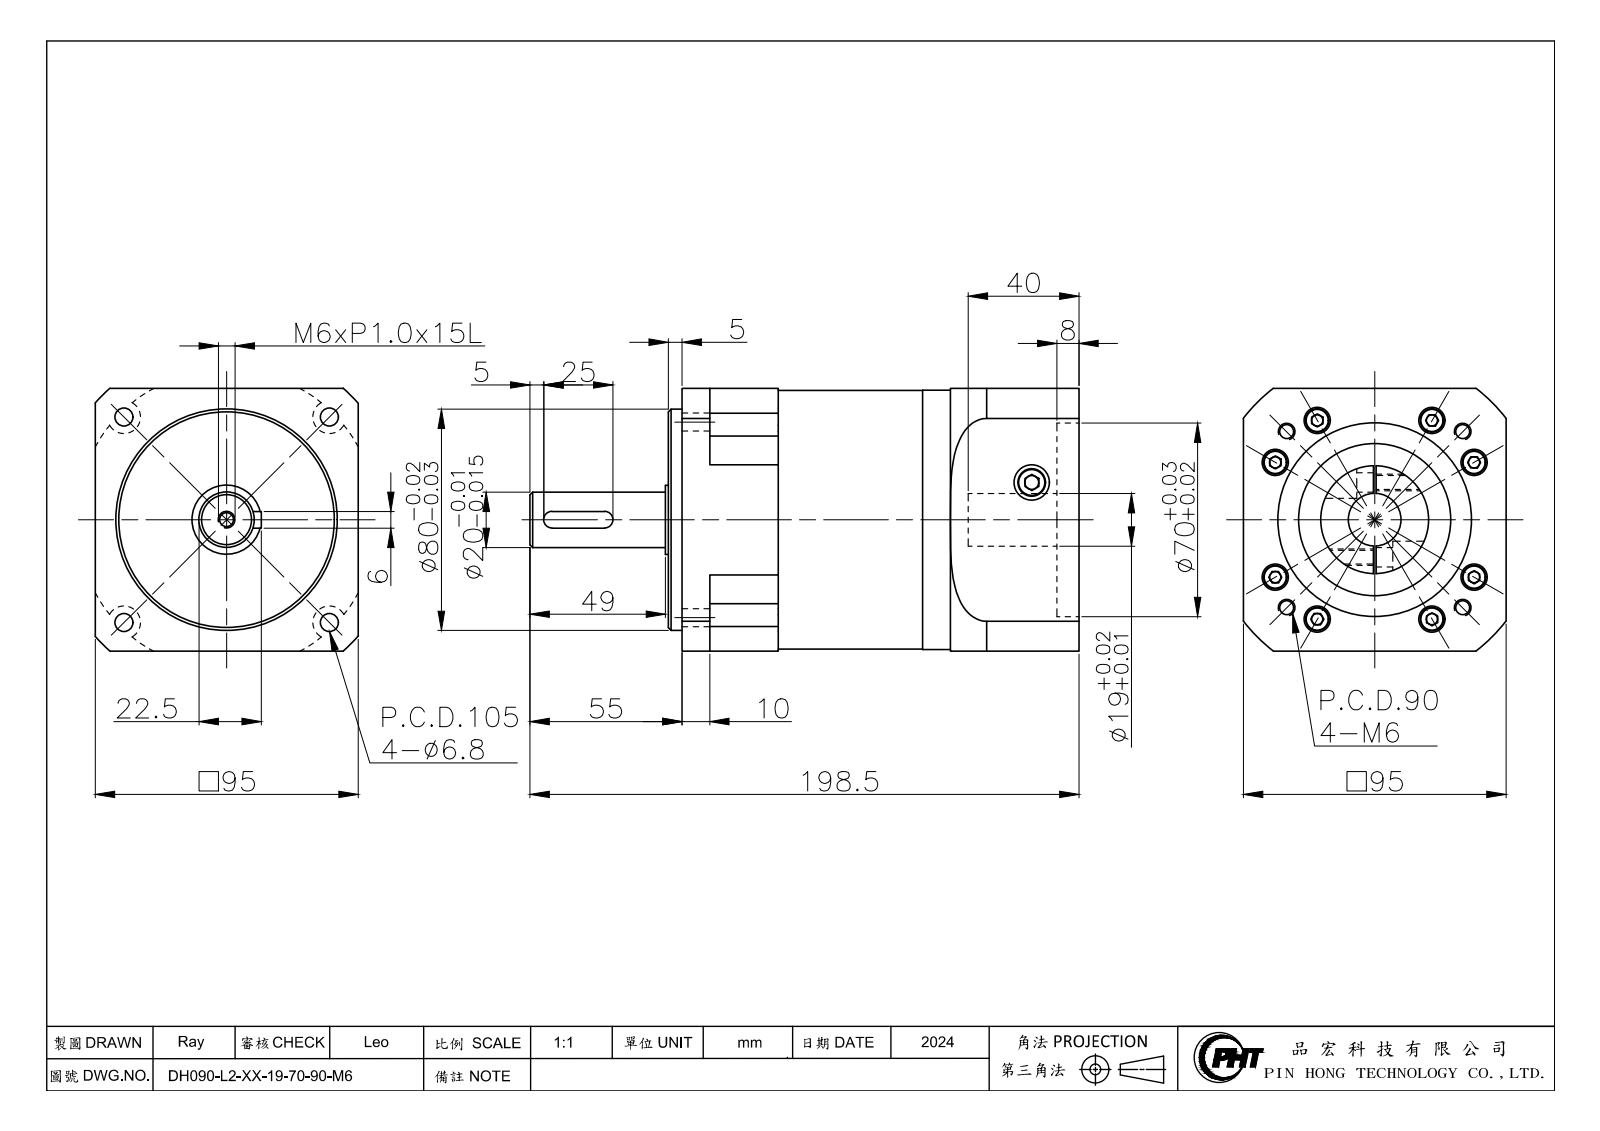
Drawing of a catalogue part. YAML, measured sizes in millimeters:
part_name: "DH090-L2-XX-19-70-90-M6_2024"
step_written_by: "SolidWorks 2016 (CONFIG_CONTROL_DESIGN)"
units: millimeters
bodies: {solids: 1, faces: 270, planar: 125, cylindrical: 115, other: 30}
overall_size: [198.5, 95, 95]
volume: 1050000
surface_area: 101726
round_holes:
  - {diameter: 5.2, count: 8}
  - {diameter: 9.5, count: 8}
  - {diameter: 5, count: 5}
  - {diameter: 6.8, count: 4}
  - {diameter: 12.7, count: 2}
  - {diameter: 19, count: 1}
  - {diameter: 55, count: 1}
  - {diameter: 70, count: 1}
round_bosses_or_shafts:
  - {diameter: 8.5, count: 8}
  - {diameter: 93.8, count: 1}
  - {diameter: 93.5, count: 1}
  - {diameter: 80, count: 1}
  - {diameter: 39, count: 1}
  - {diameter: 25, count: 1}
  - {diameter: 20, count: 1}
partial_cylinders:
  - {radius: 6, count: 4}
  - {radius: 3, count: 2}
  - {radius: 52, count: 1}
  - {radius: 60, count: 1}
  - {radius: 63.5, count: 1}
face_to_face_distances: [95, 148.5, 5, 143.5, 8, 32, 1, 140.5, 40, 103.5]
hole_center_spacings: [41.5, 11.81, 16.41, 52.73, 57.88, 58.69, 68.66, 69.14]
